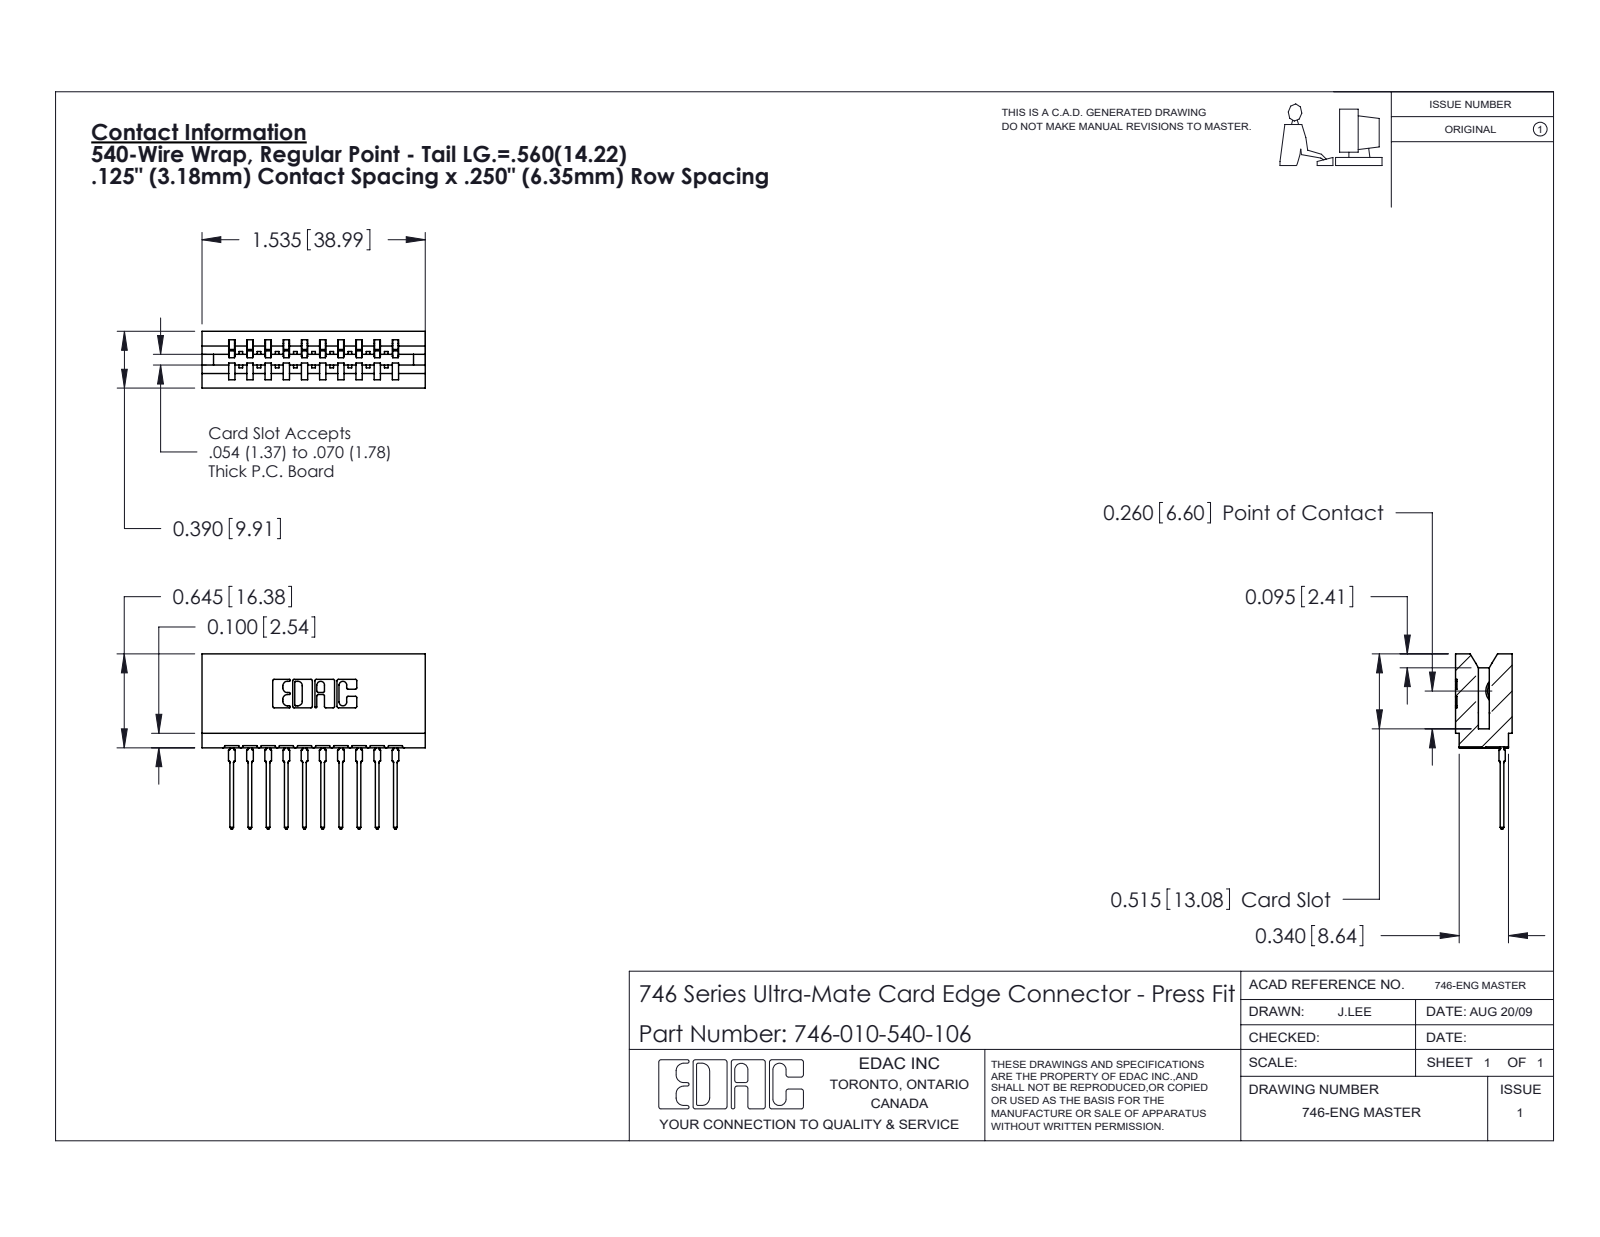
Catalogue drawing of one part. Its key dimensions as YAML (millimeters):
part_name: "746-292-001_540; 746 Part_.515 Slot Depth - 06; 746-010-540-106"
step_written_by: "SolidWorks 2020 (CONFIG_CONTROL_DESIGN)"
units: millimeters
bodies: {solids: 11, faces: 1178, planar: 686, cylindrical: 232, other: 260}
overall_size: [39, 30.6, 9.9]
volume: 4290
surface_area: 5961
partial_cylinders:
  - {radius: 0.3, count: 22}
  - {radius: 0.5, count: 20}
  - {radius: 0.4, count: 11}
  - {radius: 0.2, count: 6}
  - {radius: 0.8, count: 6}
  - {radius: 0.1, count: 4}
  - {radius: 0.3, count: 4}
  - {radius: 0.7, count: 3}
face_to_face_distances: [6.4, 8.5, 12.7, 1.4, 1.1, 3.2, 7.4, 19.1, 9.9, 9.5]
